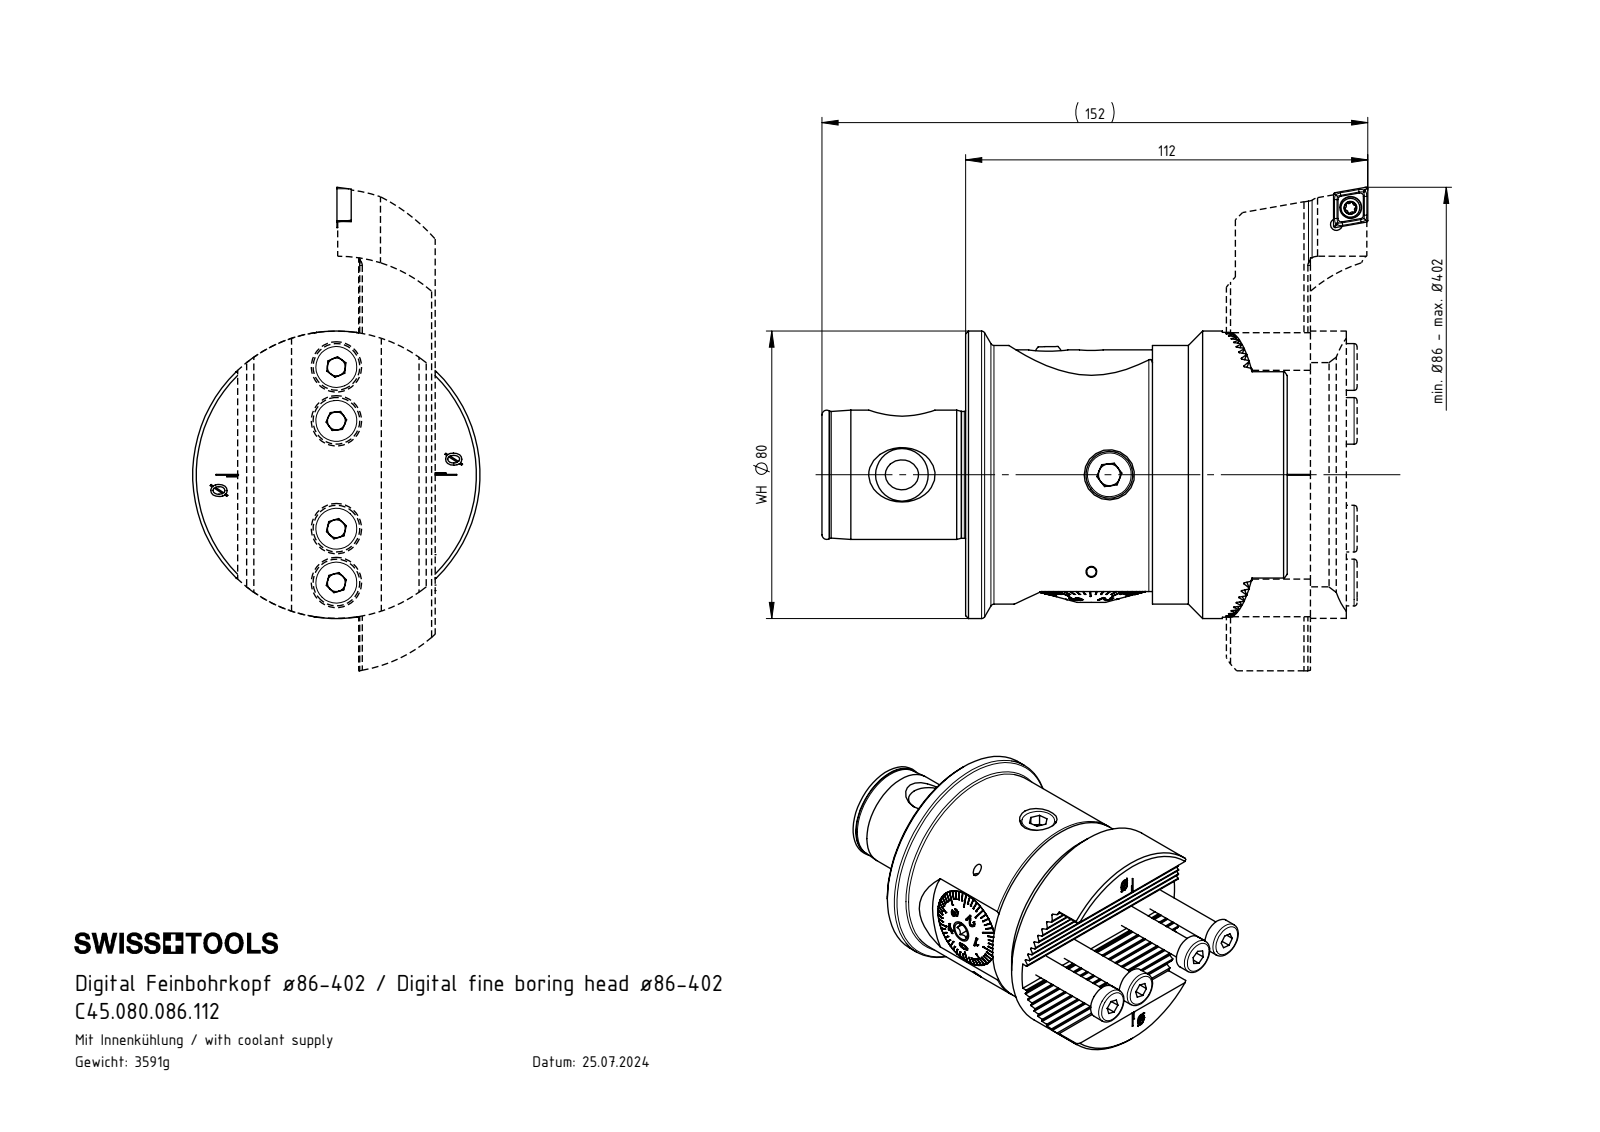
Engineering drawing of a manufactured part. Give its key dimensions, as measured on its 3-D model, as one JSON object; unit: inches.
{"part_name": "F00-BG1.001.046_A; F00-BG6.001.008_A; DIN 3771 - 24x1.5; F72-BG3.003.013_A (+8 more)", "step_written_by": "SolidWorks 2022 (AUTOMOTIVE_DESIGN)", "units": "inches", "bodies": {"solids": 26, "faces": 1187, "planar": 555, "cylindrical": 270, "other": 362}, "overall_size": [5.865, 3.15, 3.15], "volume_in3": 21.76, "surface_area_in2": 146.2, "round_holes": [[0.197, 5], [0.413, 5], [0.126, 4], [0.268, 4], [0.276, 4], [0.394, 4], [0.118, 2], [0.13, 2], [0.236, 2], [0.028, 1], [0.039, 1], [0.124, 1]], "round_bosses_or_shafts": [[0.315, 6], [0.075, 6], [0.512, 5], [0.394, 4], [0.236, 4], [3.15, 1], [2.835, 1], [1.417, 1]], "partial_cylinders_radius": [[0.008, 16], [0.047, 8], [0.043, 6], [0.122, 2], [0.193, 2], [0.02, 1], [0.083, 1], [0.098, 1]], "face_to_face_distances": [2.047, 0.094, 0.187, 0.281, 0.281, 0.375, 0.188, 0.469, 0.563, 2.461], "hole_center_spacings": [0.472, 0.25, 0.474, 0.591, 0.726, 0.787, 1.309, 1.346]}
